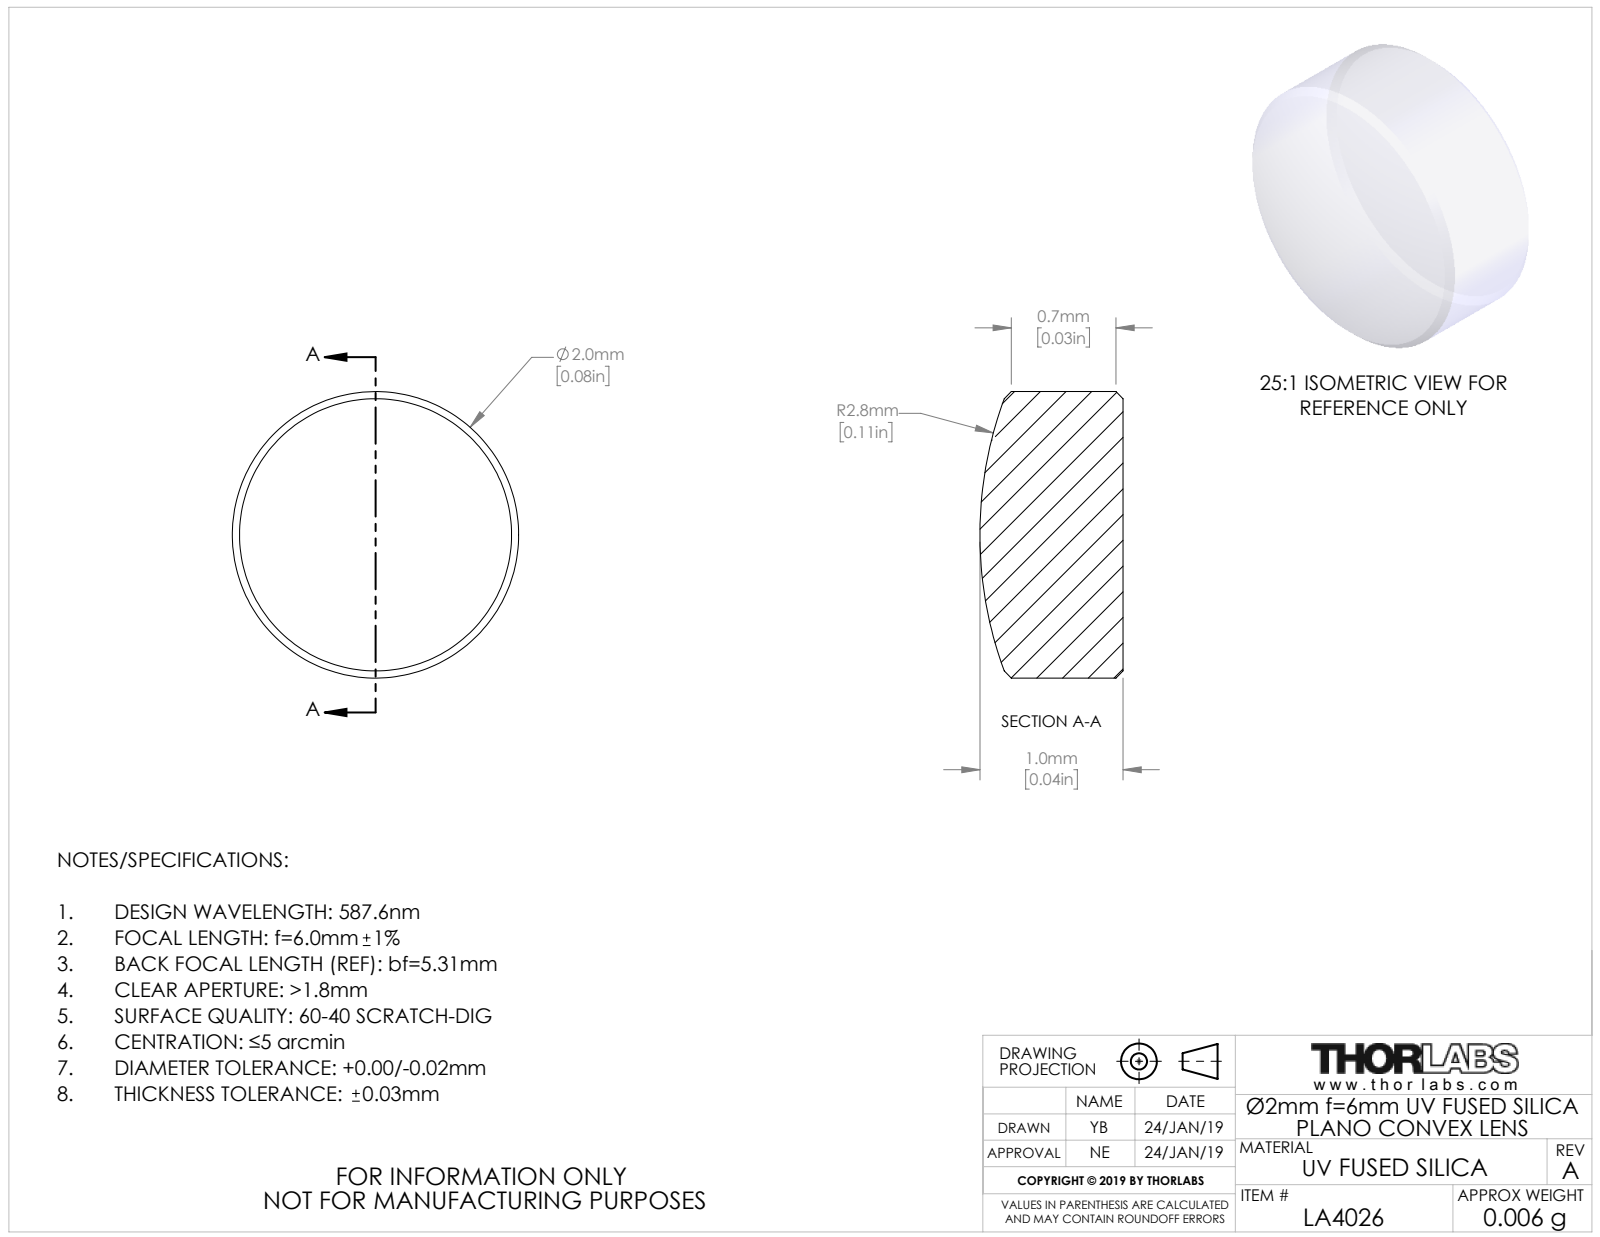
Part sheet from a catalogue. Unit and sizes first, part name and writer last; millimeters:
Units: millimetres
Overall size (bounding box): 2 × 2 × 1
Round bosses / shafts (diameter × count): ⌀2 ×1
Volume: 3 mm³ · Surface area: 11 mm²
Bodies: 1 solid, 9 faces (1 planar, 2 cylindrical, 6 other)
Part name (STEP PRODUCT): TTN162792-E0W
STEP written by: SolidWorks 2018 (CONFIG_CONTROL_DESIGN)
